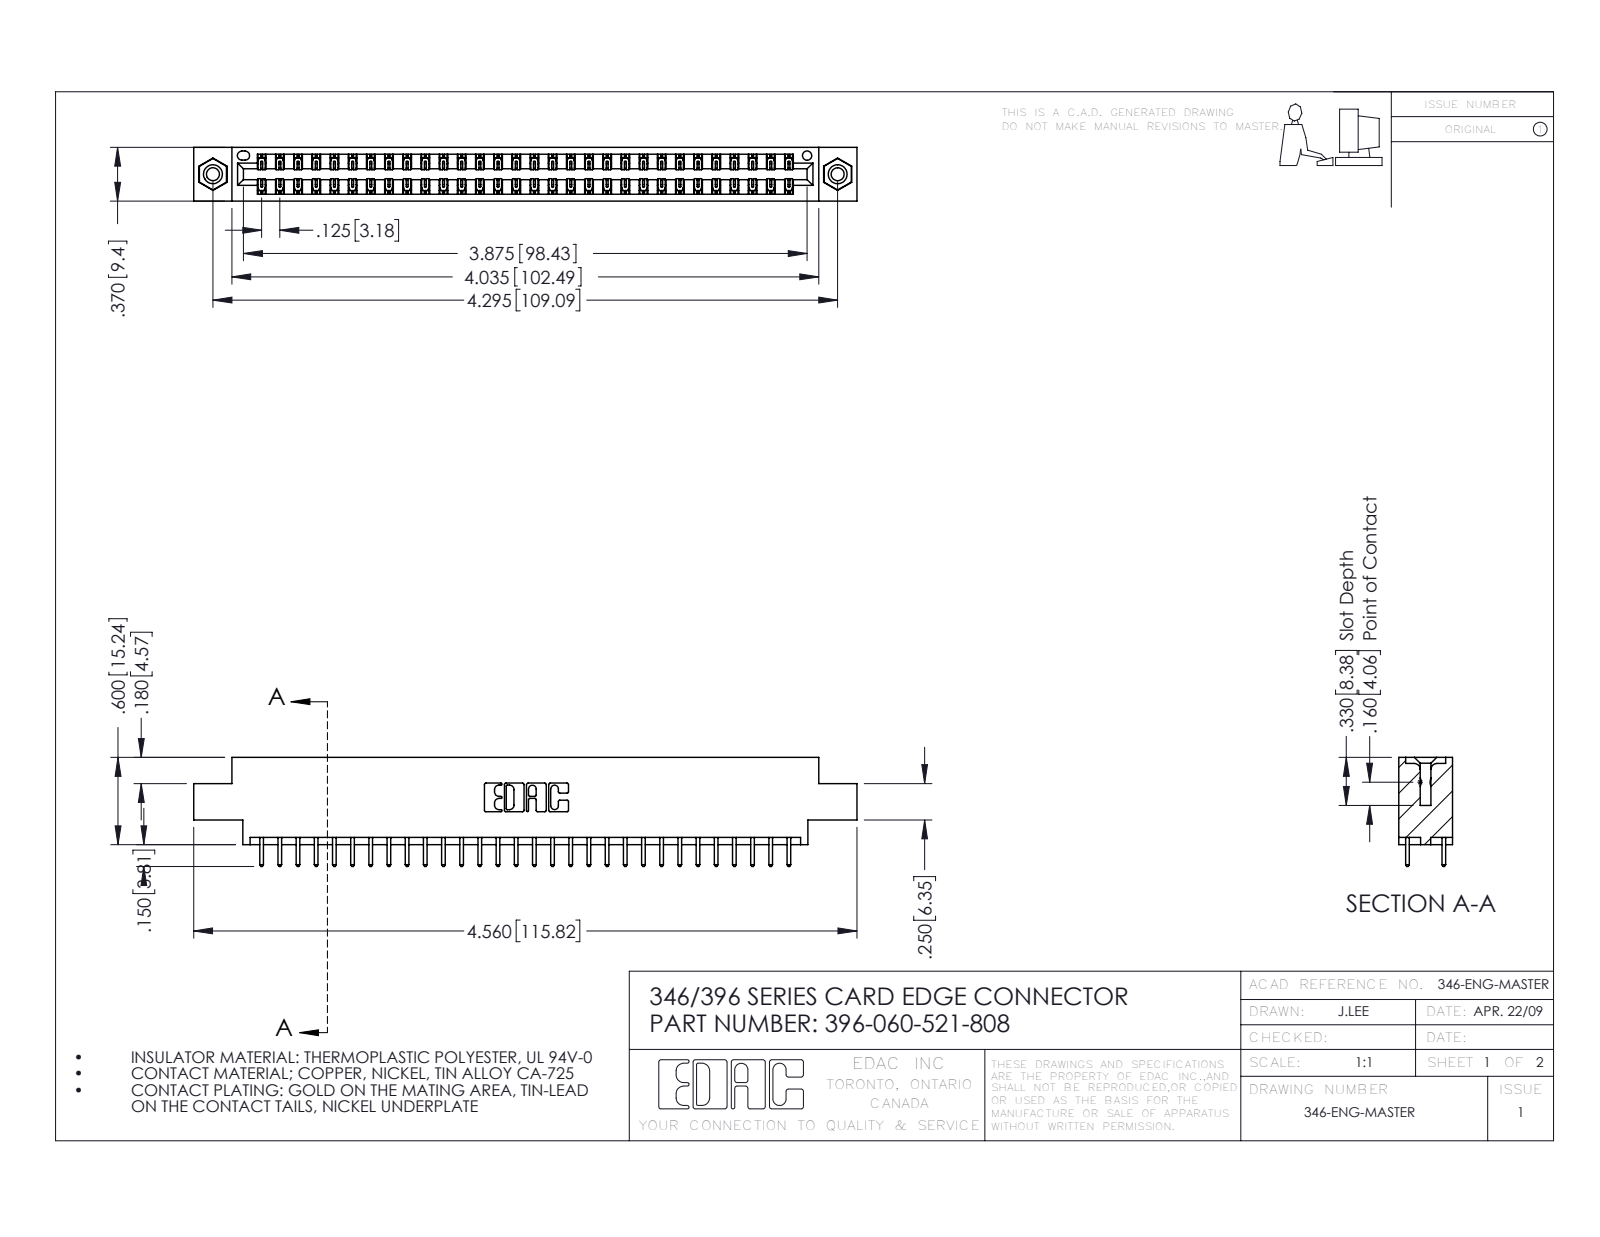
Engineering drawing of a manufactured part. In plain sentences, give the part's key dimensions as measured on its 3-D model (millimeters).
The part is named "345-292-001_345-293-121; 396-060-521-808; 346 Part_0.170 Offset - 0.156 Dia-TI; 345-250-001_345-250-003-102". Its 3-D file was written by "SolidWorks 2016 (CONFIG_CONTROL_DESIGN)". It is 63 solids with 3306 faces: 2212 planar, 1078 cylindrical and 16 other. Overall it measures 115.8 by 19.1 by 9.4 millimeters. Its volume is 11 000 cubic millimeters and its surface area 14 990 square millimeters. Round holes: 2 of diameter 2.3, 2 of diameter 3.2, 2 of diameter 4, 1 of diameter 1.6. Round bosses or shafts: 2 of diameter 3.9. Partial cylindrical surfaces (rounded edges, fillets, slot ends): 90 of radius 0.2, 60 of radius 0.3, 22 of radius 0.3, 6 of radius 0.2, 6 of radius 0.8, 3 of radius 0.7, 2 of radius 0.4, 2 of radius 0.6. The main face-to-face distances are 1.2, 8.2, 9.4, 6.4, 1.8, 7.6, 0.6, 7, 5.6, 3.8. The hole center spacings are 6.2, 103.8, 109.1.
